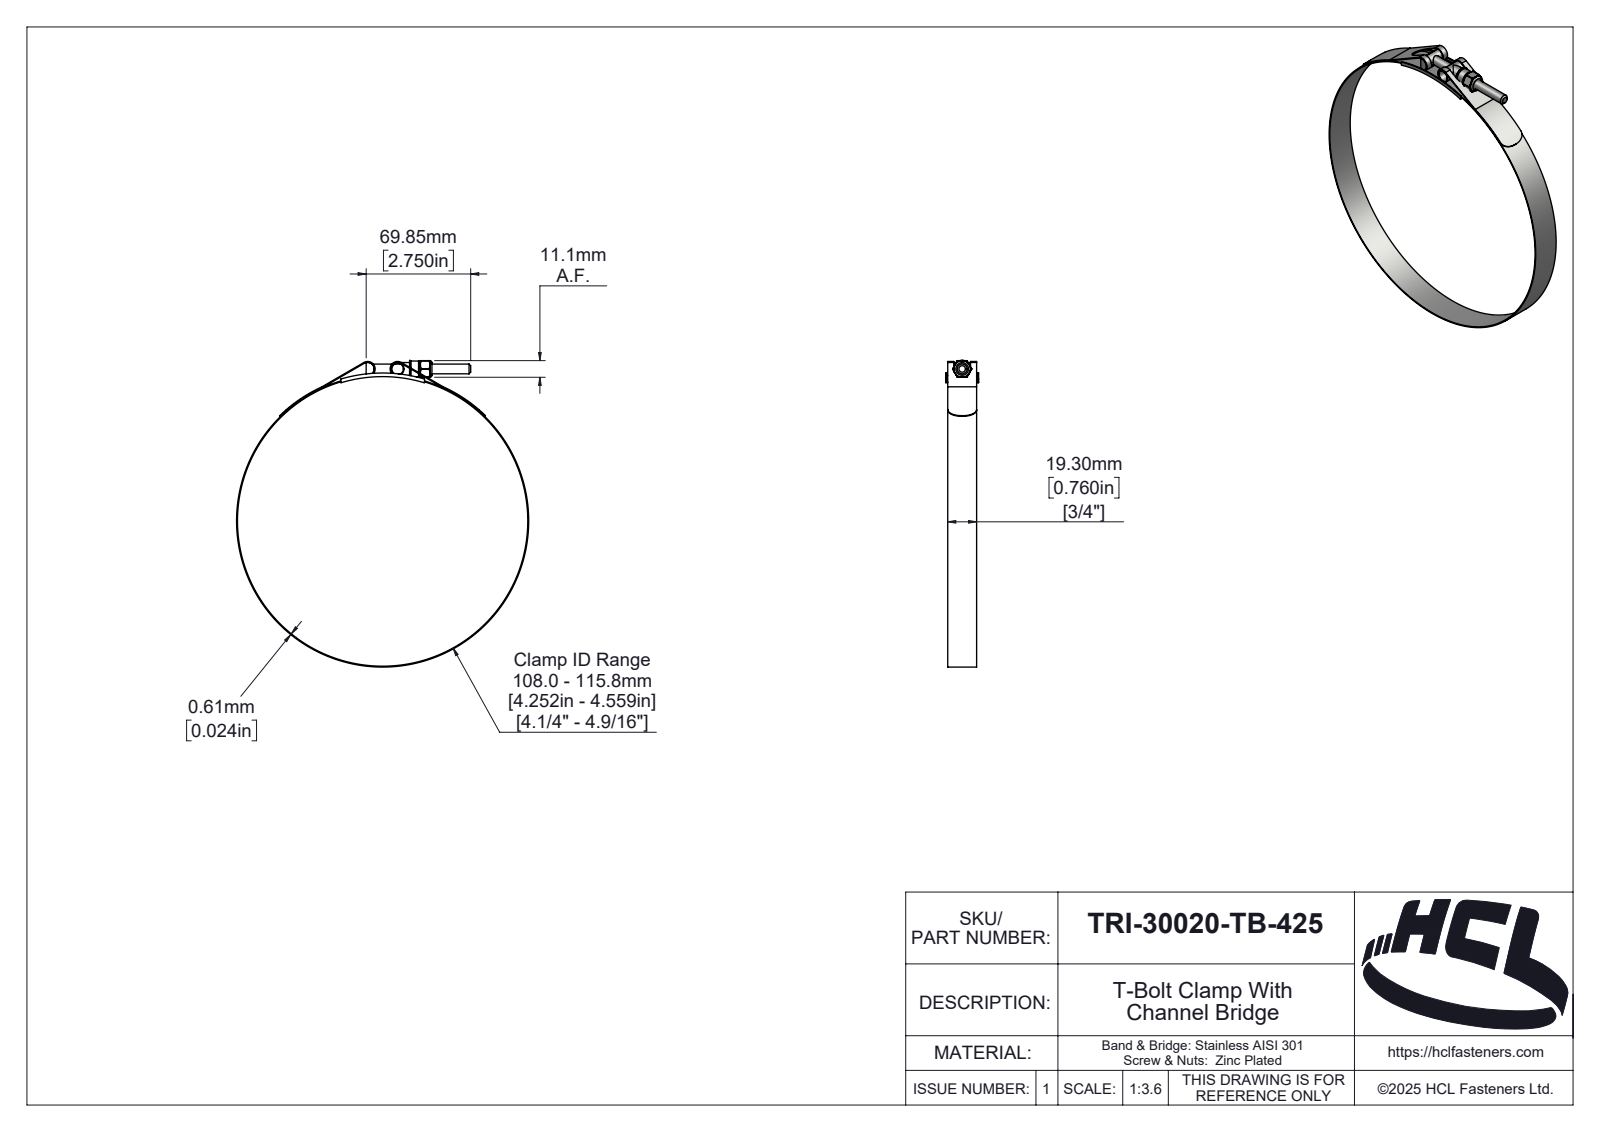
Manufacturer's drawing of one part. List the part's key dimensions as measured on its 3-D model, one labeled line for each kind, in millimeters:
Part name (STEP PRODUCT): TRI-30020-TB-425
STEP written by: SolidWorks 2025 (AUTOMOTIVE_DESIGN)
Units: millimetres
Bodies: 6 solids, 330 faces (44 planar, 122 cylindrical, 164 other)
Overall size (bounding box): 204.84 × 195.22 × 22
Volume: 13 578 mm³ · Surface area: 36 269 mm²
Round holes (diameter × count): ⌀5.4 ×1, ⌀6.35 ×1, ⌀6.5 ×1, ⌀7.58 ×1, ⌀194 ×1
Round bosses / shafts (diameter × count): ⌀8.58 ×2, ⌀195.22 ×1, ⌀10.58 ×1
Partial cylindrical surfaces — rounded edges, fillets, slot ends (radius × count): R0.39 ×6, R0.5 ×2, R4.39 ×2, R5 ×2, R0.59 ×1, R2.42 ×1, R3.03 ×1, R3.19 ×1
Main face-to-face distances: 0.61, 19.3, 1.35, 20.65, 0.74, 21.39, 20.04, 22, 11.11, 20.78
Hole centre spacings: 102
